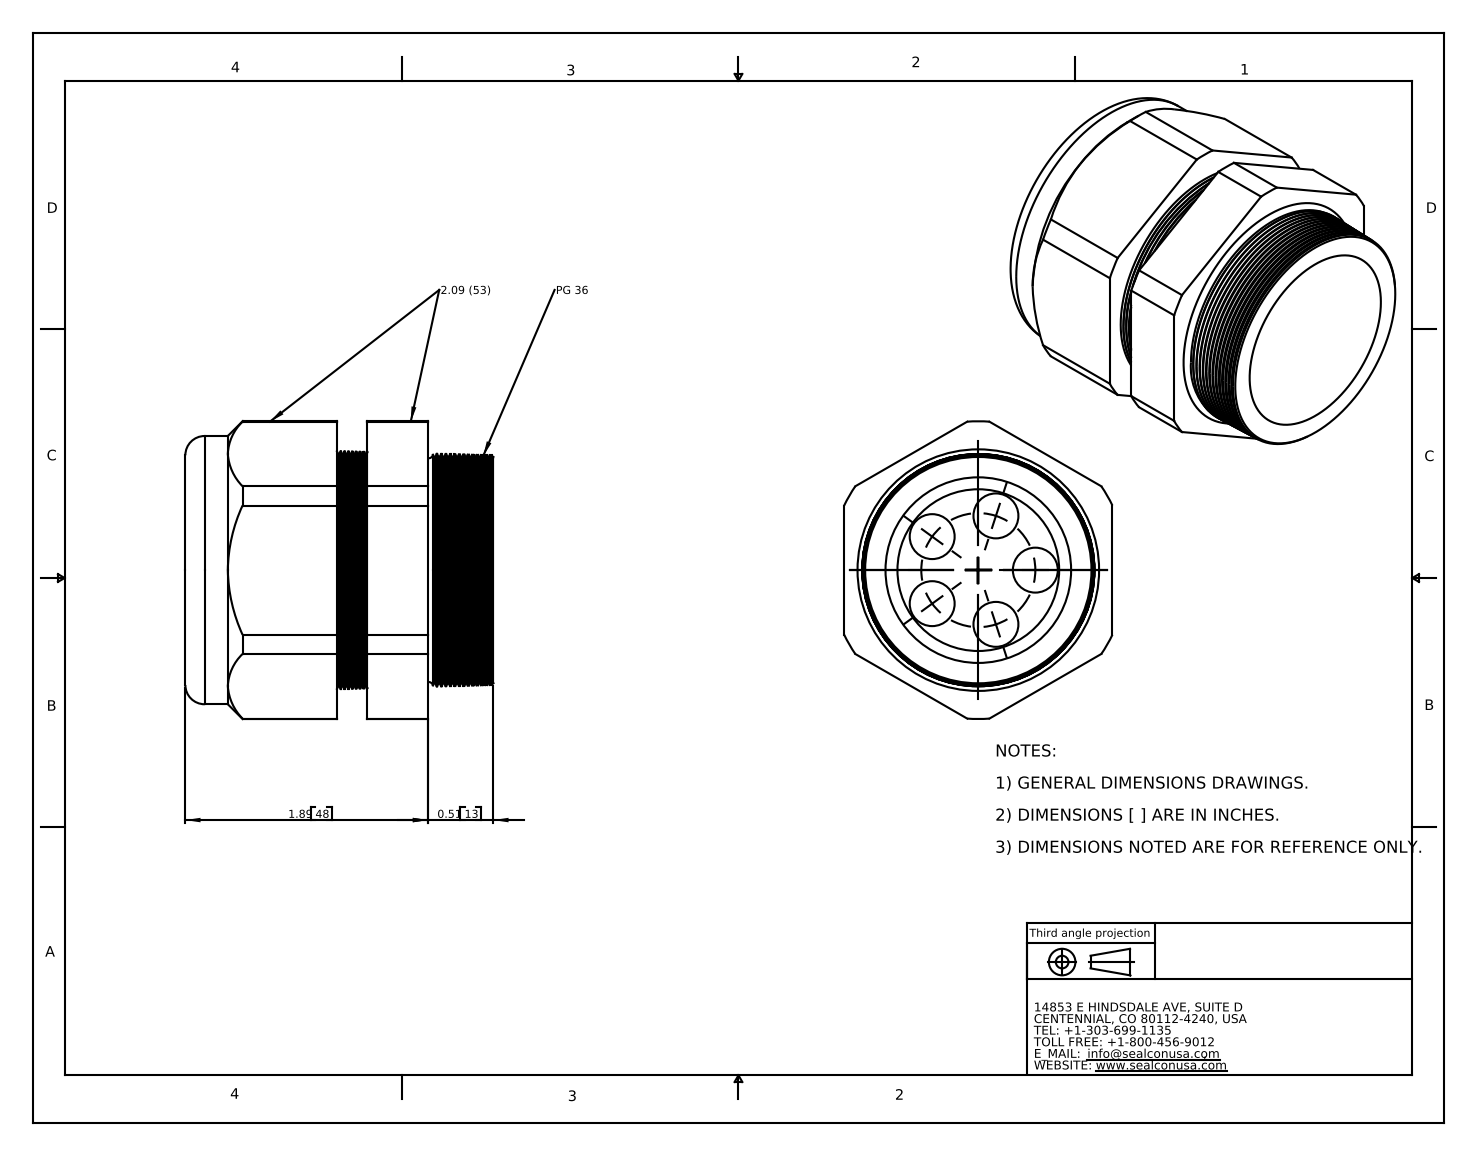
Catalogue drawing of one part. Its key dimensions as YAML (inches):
part_name: "CD36A1-GY"
step_written_by: "SolidWorks 2007 (CONFIG_CONTROL_DESIGN)"
units: inches
bodies: {solids: 2, faces: 199, planar: 21, cylindrical: 30, other: 148}
overall_size: [2.4, 2.32, 2.09]
volume: 5.078
surface_area: 41.52
round_holes:
  - {diameter: 0.35, count: 5}
  - {diameter: 1.24, count: 1}
  - {diameter: 1.26, count: 1}
round_bosses_or_shafts:
  - {diameter: 2.09, count: 1}
partial_cylinders:
  - {radius: 1.16, count: 1}
face_to_face_distances: [2.09, 1.418, 1.181, 0.237, 1.89, 0.709, 0.472, 2.4, 1.219, 0.982]
hole_center_spacings: [0.444, 0.522, 0.845, 0.845, 0.444, 0.522]
